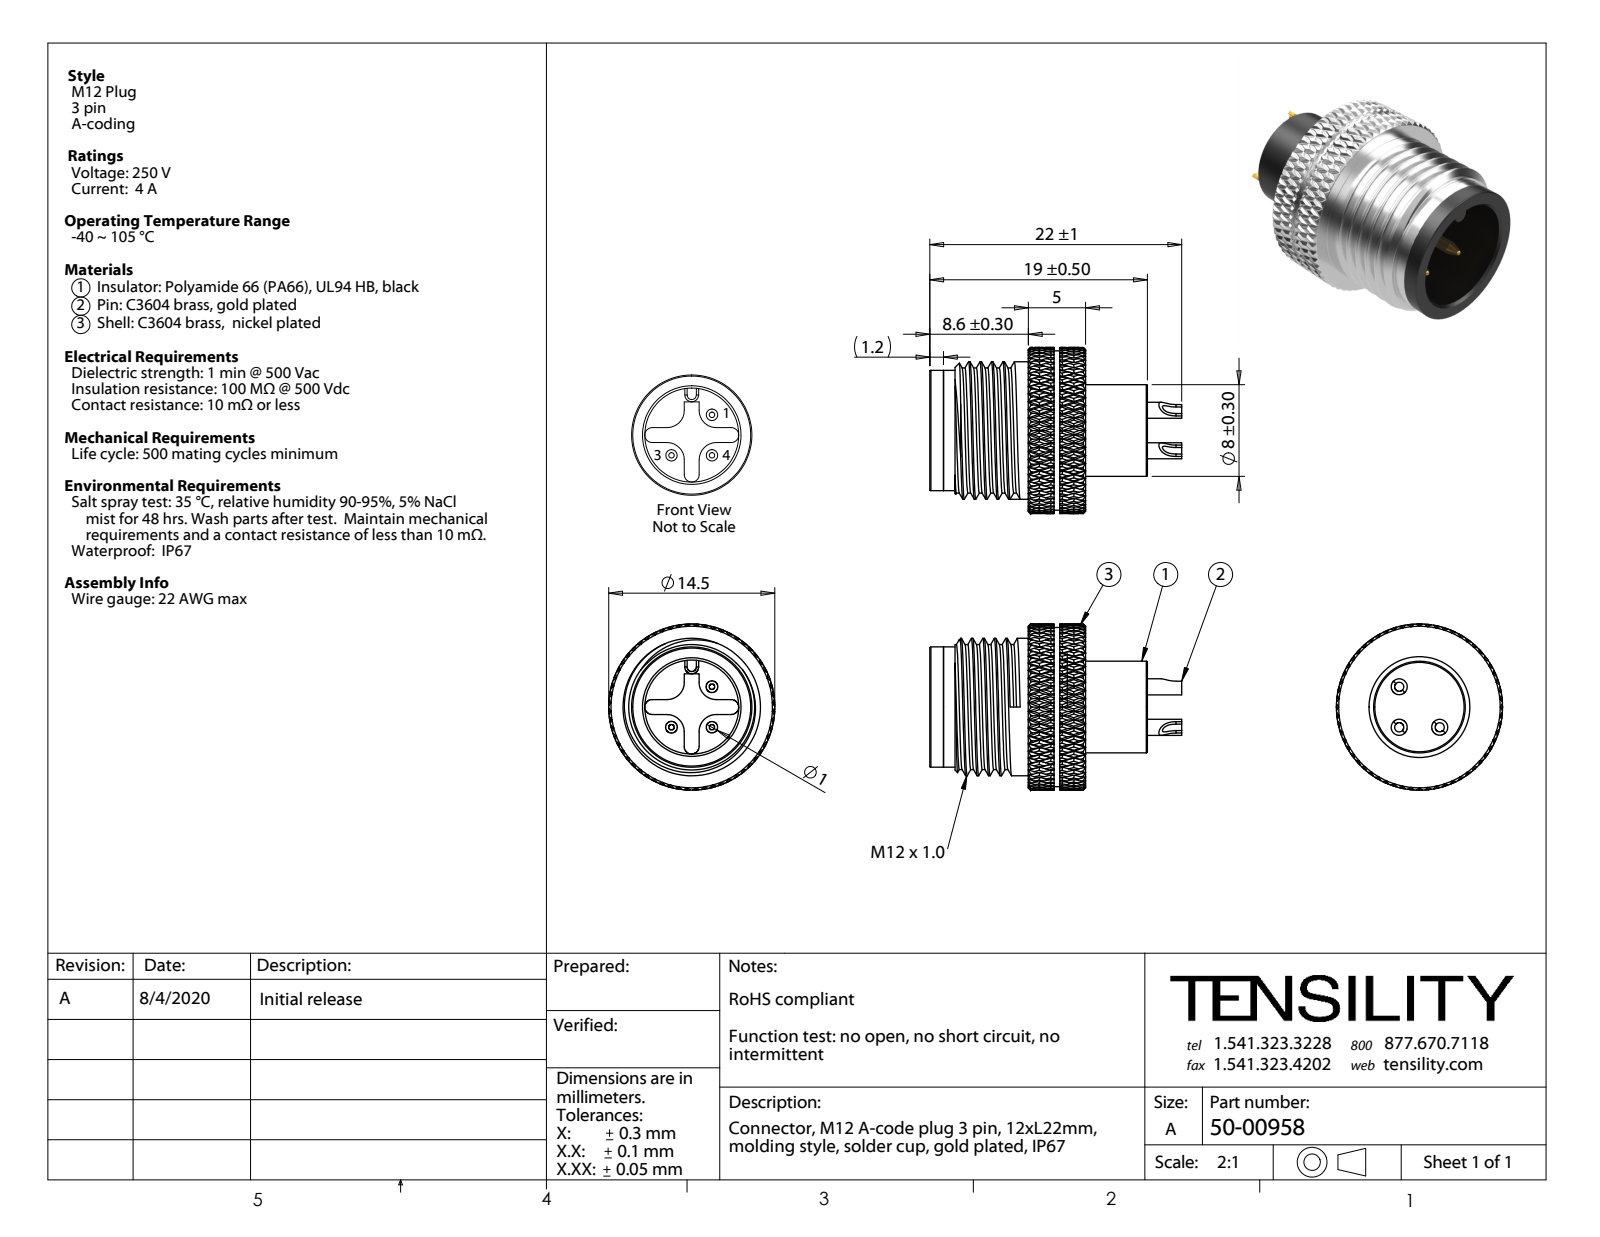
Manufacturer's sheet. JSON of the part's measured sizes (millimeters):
{"part_name": "50-00958-03; 50-00958; 50-00958-02; 50-00958-01", "step_written_by": "SolidWorks 2015 (CONFIG_CONTROL_DESIGN)", "units": "millimeters", "bodies": {"solids": 5, "faces": 205, "planar": 53, "cylindrical": 93, "other": 59}, "overall_size": [22, 14.5, 14.5], "volume_mm3": 1434, "surface_area_mm2": 2527, "round_holes": [[0.8, 3], [1, 3], [8.2, 1], [8.8, 1], [9.5, 1]], "round_bosses_or_shafts": [[1.4, 3], [14.5, 1], [13.9, 1], [12, 1], [10.5, 1], [9.3, 1], [8, 1]], "partial_cylinders_radius": [[1.5, 4], [0.65, 3], [1.96, 3], [0.2, 2], [0.6, 1]], "face_to_face_distances": [10.4, 5, 5.4, 9.5, 0.5, 10, 7.4, 12.4, 17.8, 7.8], "hole_center_spacings": [2.5, 3.54, 5.01]}
